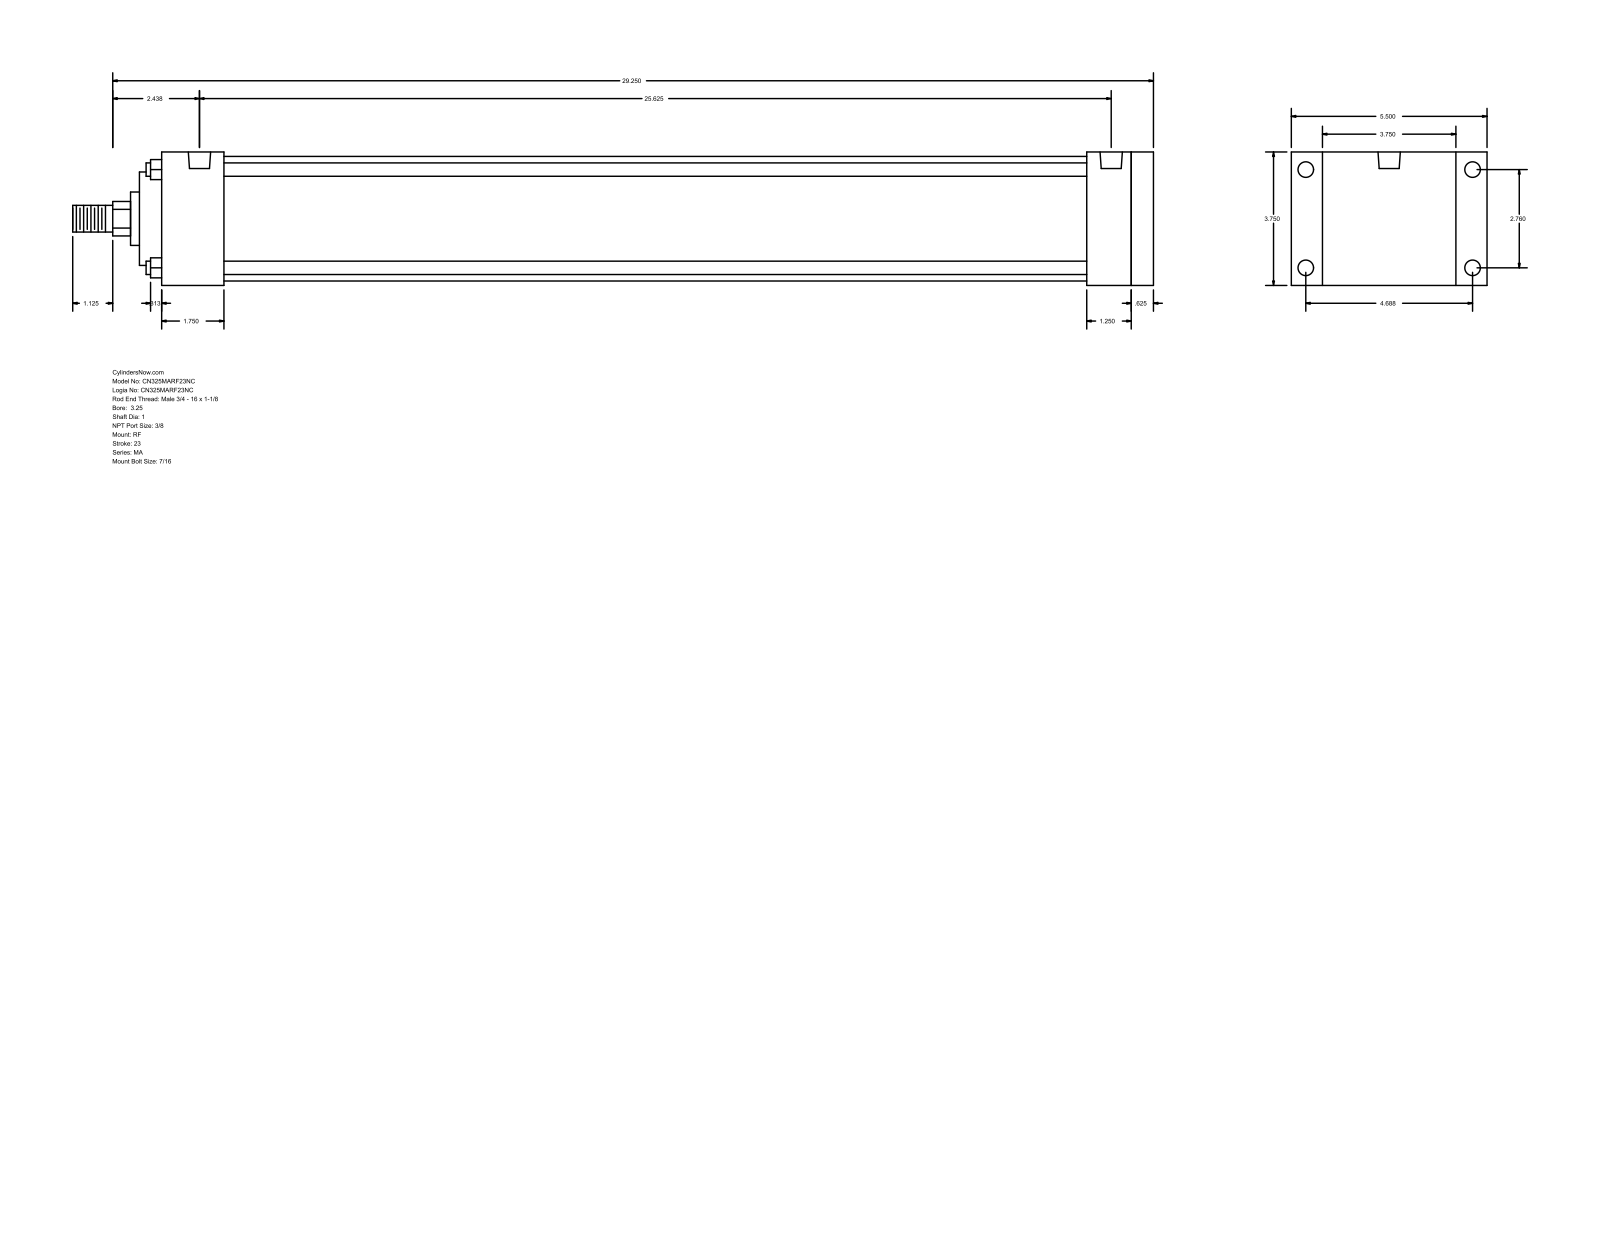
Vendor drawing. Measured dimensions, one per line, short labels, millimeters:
name: MA_RF__0325_1
written by: GSSL Pune (CONFIG_CONTROL_DESIGN)
unit: mm
bodies: 0 solids, 94 faces (65 planar, 29 cylindrical, 0 other)
size: 771.52 × 139.7 × 95.25
holes: 8× ⌀11.11, 2× ⌀15.93
bosses: 4× ⌀9.53, 1× ⌀88.9, 1× ⌀66.67, 1× ⌀38.1, 1× ⌀25.4, 1× ⌀19.05
rounds: 1× R12.29
face distances: 95.24, 708.03, 15.87, 692.16, 22.23, 117.47, 47.62, 723.9, 660.41, 31.75
hole spacings: 70.1, 119.06, 138.16, 641.35, 4.76, 4.77, 646.11, 646.12
